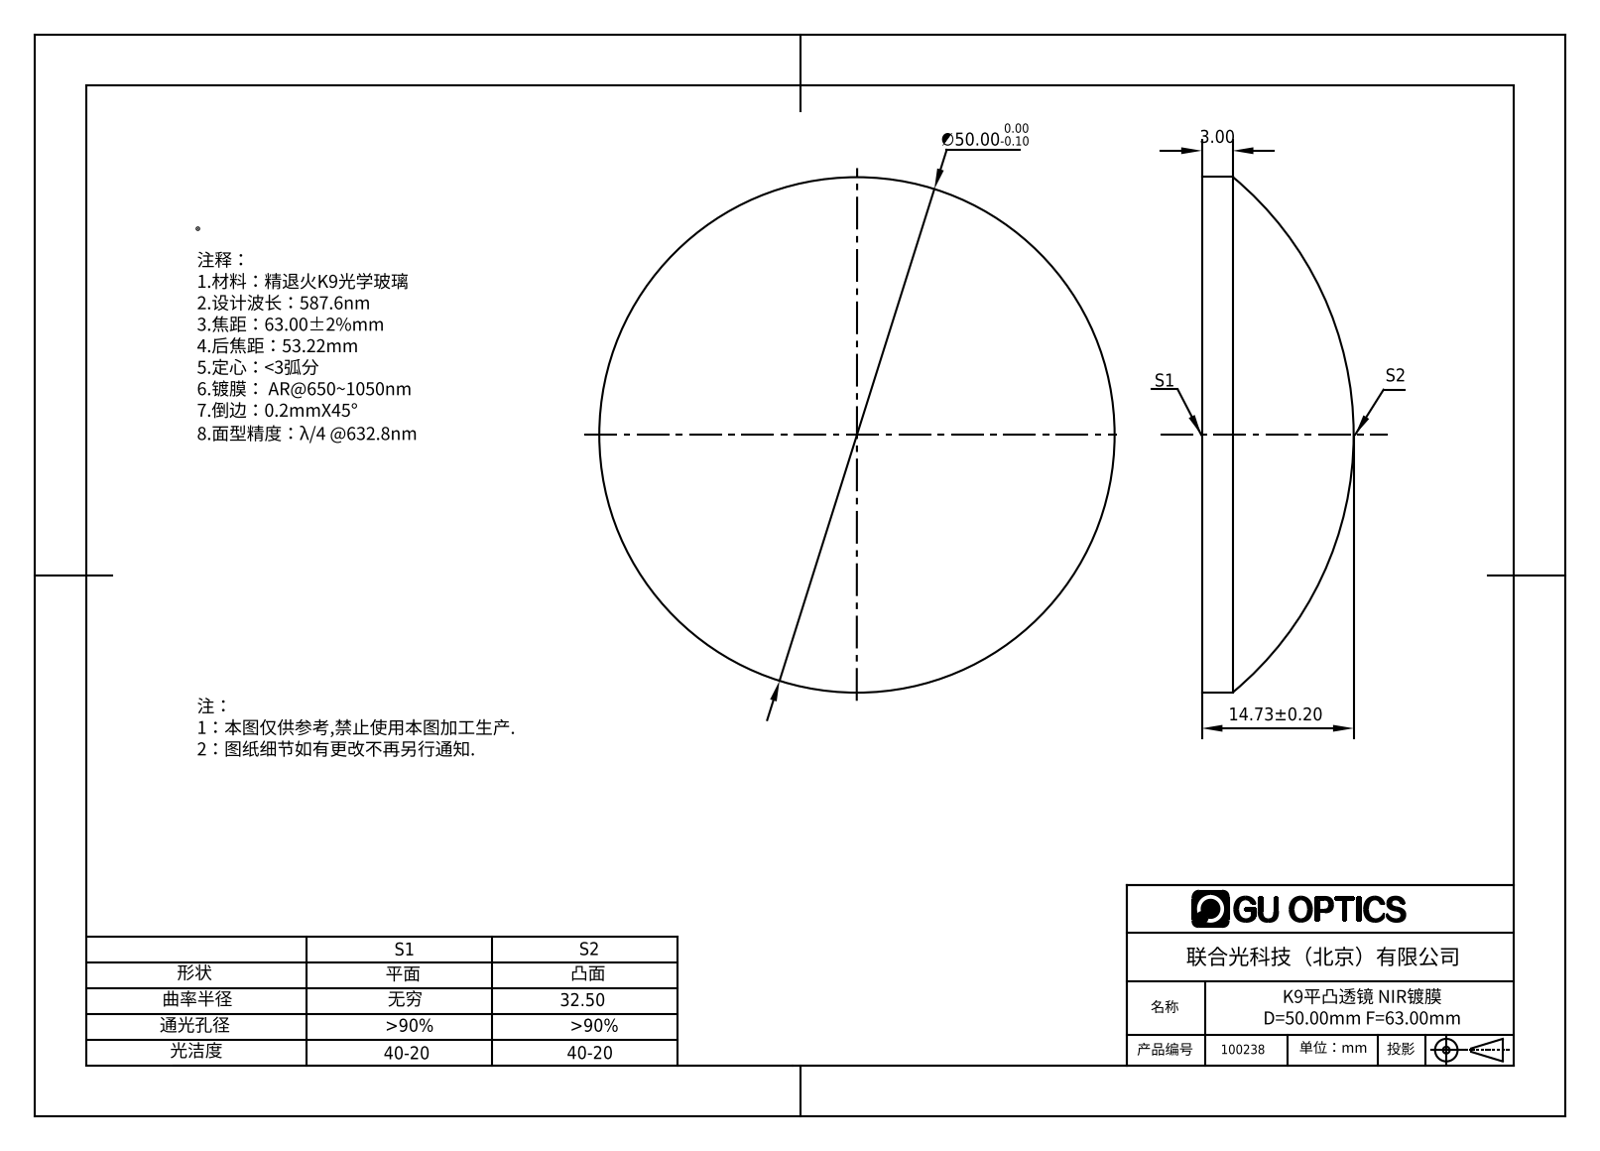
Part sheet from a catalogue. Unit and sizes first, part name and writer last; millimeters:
Units: millimetres
Overall size (bounding box): 50 × 50 × 14.73
Round bosses / shafts (diameter × count): ⌀50 ×1
Volume: 18 251 mm³ · Surface area: 4 830 mm²
Bodies: 1 solid, 5 faces (1 planar, 2 cylindrical, 2 other)
Part name (STEP PRODUCT): 100238
STEP written by: SolidWorks 2016 (AUTOMOTIVE_DESIGN)
